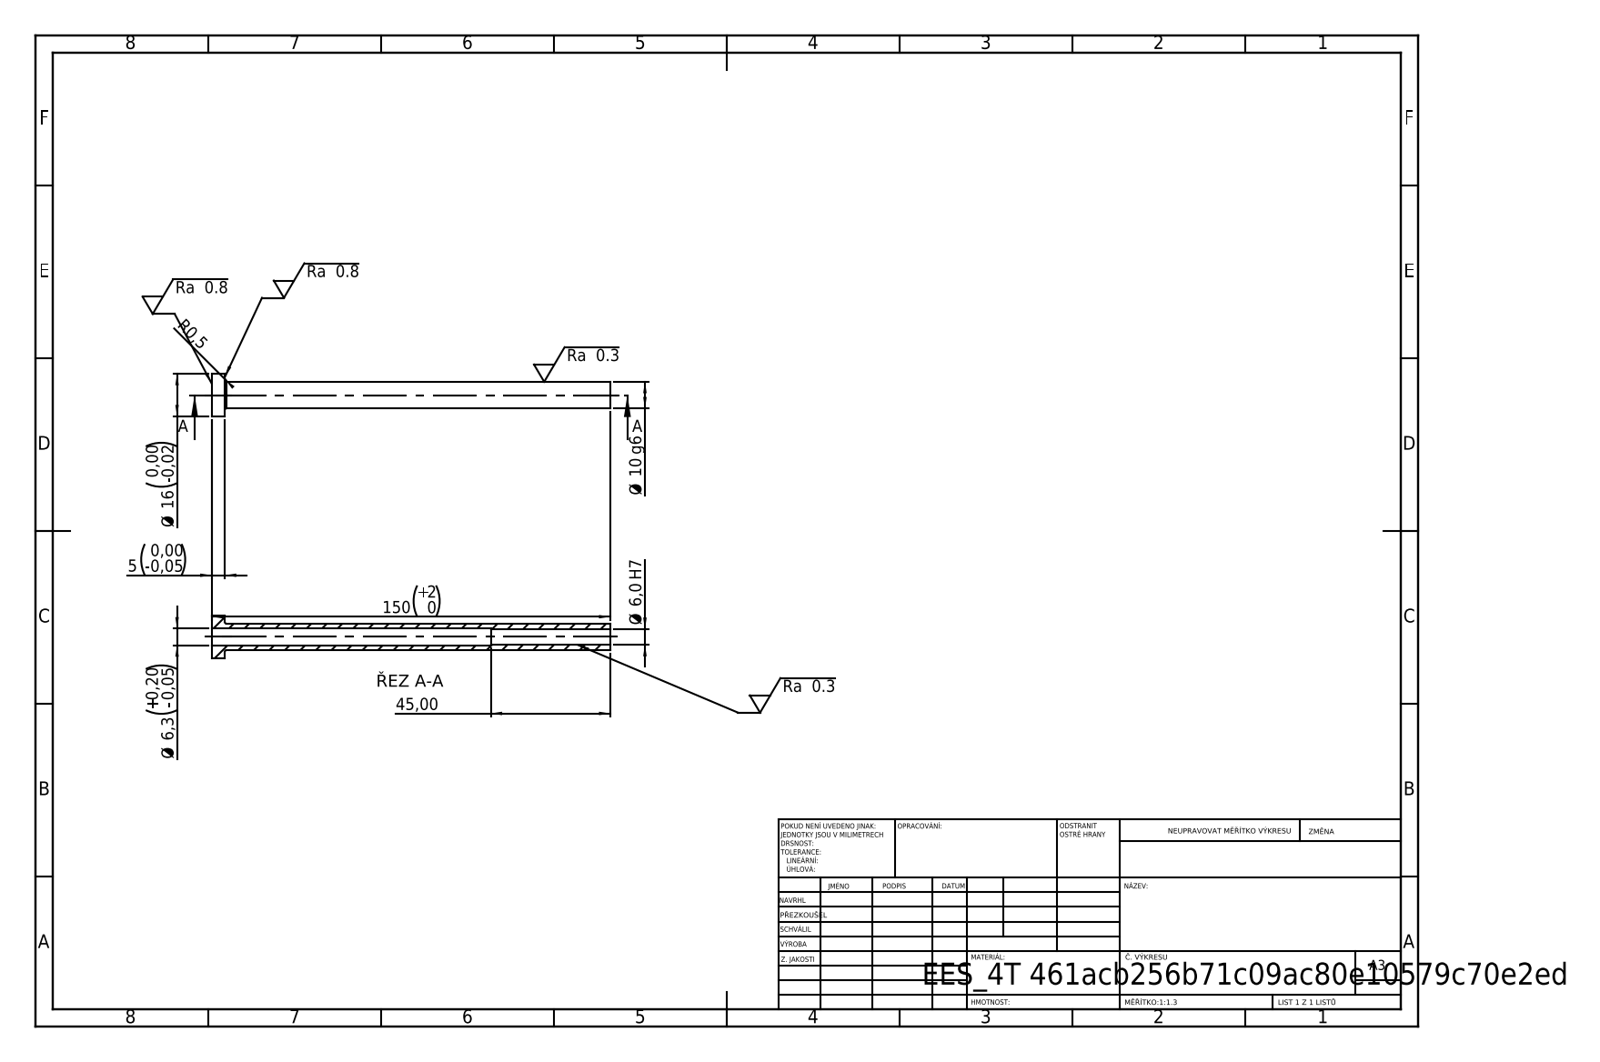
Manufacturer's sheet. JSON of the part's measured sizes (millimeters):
{"step_written_by": "SolidWorks 2019 (CONFIG_CONTROL_DESIGN)", "units": "millimeters", "bodies": {"solids": 1, "faces": 14, "planar": 4, "cylindrical": 8, "other": 2}, "overall_size": [150, 16, 16], "volume_mm3": 7850, "surface_area_mm2": 8072, "round_holes": [[6, 1], [6.3, 1]], "round_bosses_or_shafts": [[16, 1], [10, 1]], "face_to_face_distances": [5, 150, 145, 105, 100, 45]}
